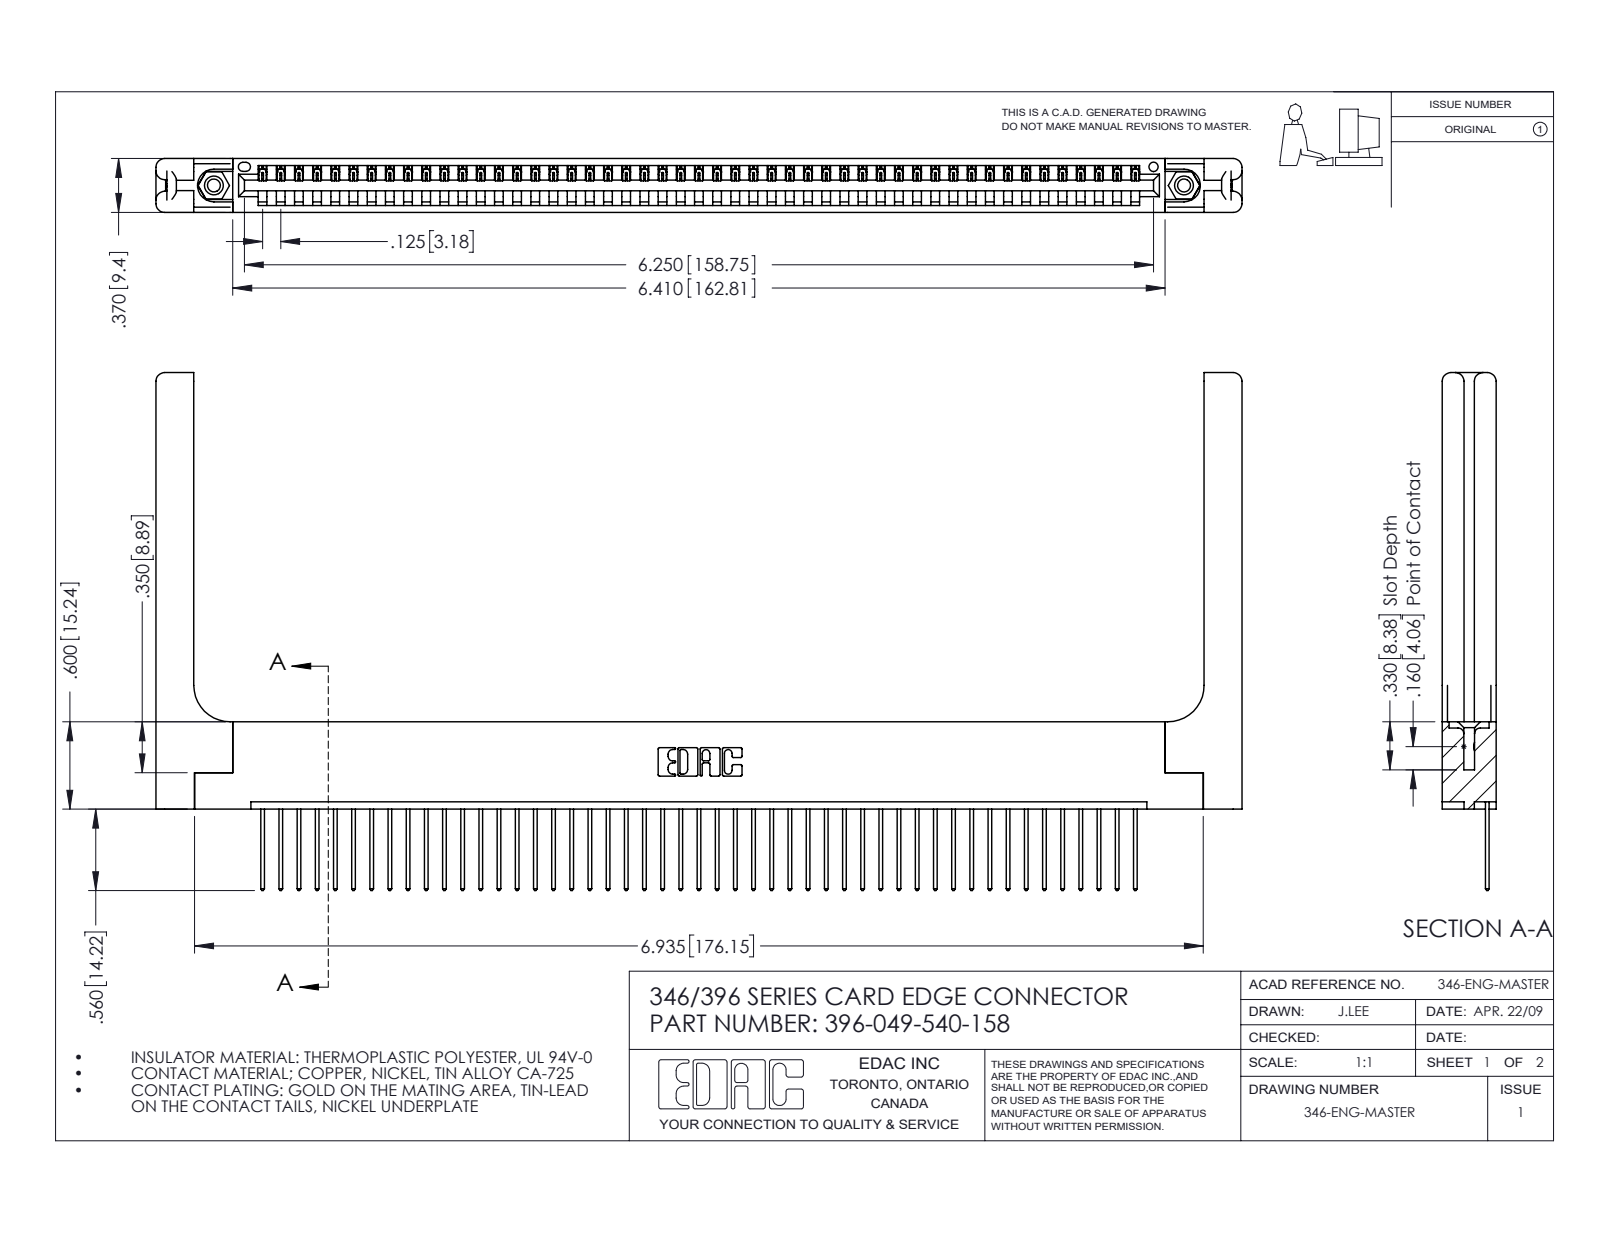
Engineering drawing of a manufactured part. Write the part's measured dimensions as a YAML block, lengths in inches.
part_name: "345-250-001_345-250-001-102; 345-292-001_345-293-140; 346 Part_Flush Mounting Lugs - 0.156 Dia-TH; 396-049-540-158 (+1 more)"
step_written_by: "SolidWorks 2016 (CONFIG_CONTROL_DESIGN)"
units: inches
bodies: {solids: 54, faces: 3220, planar: 2184, cylindrical: 976, other: 60}
overall_size: [7.466, 3.56, 0.37]
volume: 1.574
surface_area: 44.27
round_holes:
  - {diameter: 0.089, count: 2}
  - {diameter: 0.125, count: 2}
  - {diameter: 0.156, count: 2}
  - {diameter: 0.064, count: 1}
round_bosses_or_shafts:
  - {diameter: 0.155, count: 2}
partial_cylinders:
  - {radius: 0.006, count: 98}
  - {radius: 0.01, count: 98}
  - {radius: 0.01, count: 22}
  - {radius: 0.06, count: 16}
  - {radius: 0.007, count: 6}
  - {radius: 0.031, count: 6}
  - {radius: 0.026, count: 3}
  - {radius: 0.03, count: 2}
face_to_face_distances: [0.37, 0.048, 0.322, 0.072, 0.148, 0.25, 0.15, 0.298, 0.025, 0.222]
hole_center_spacings: [0.246, 6.461, 6.67]
